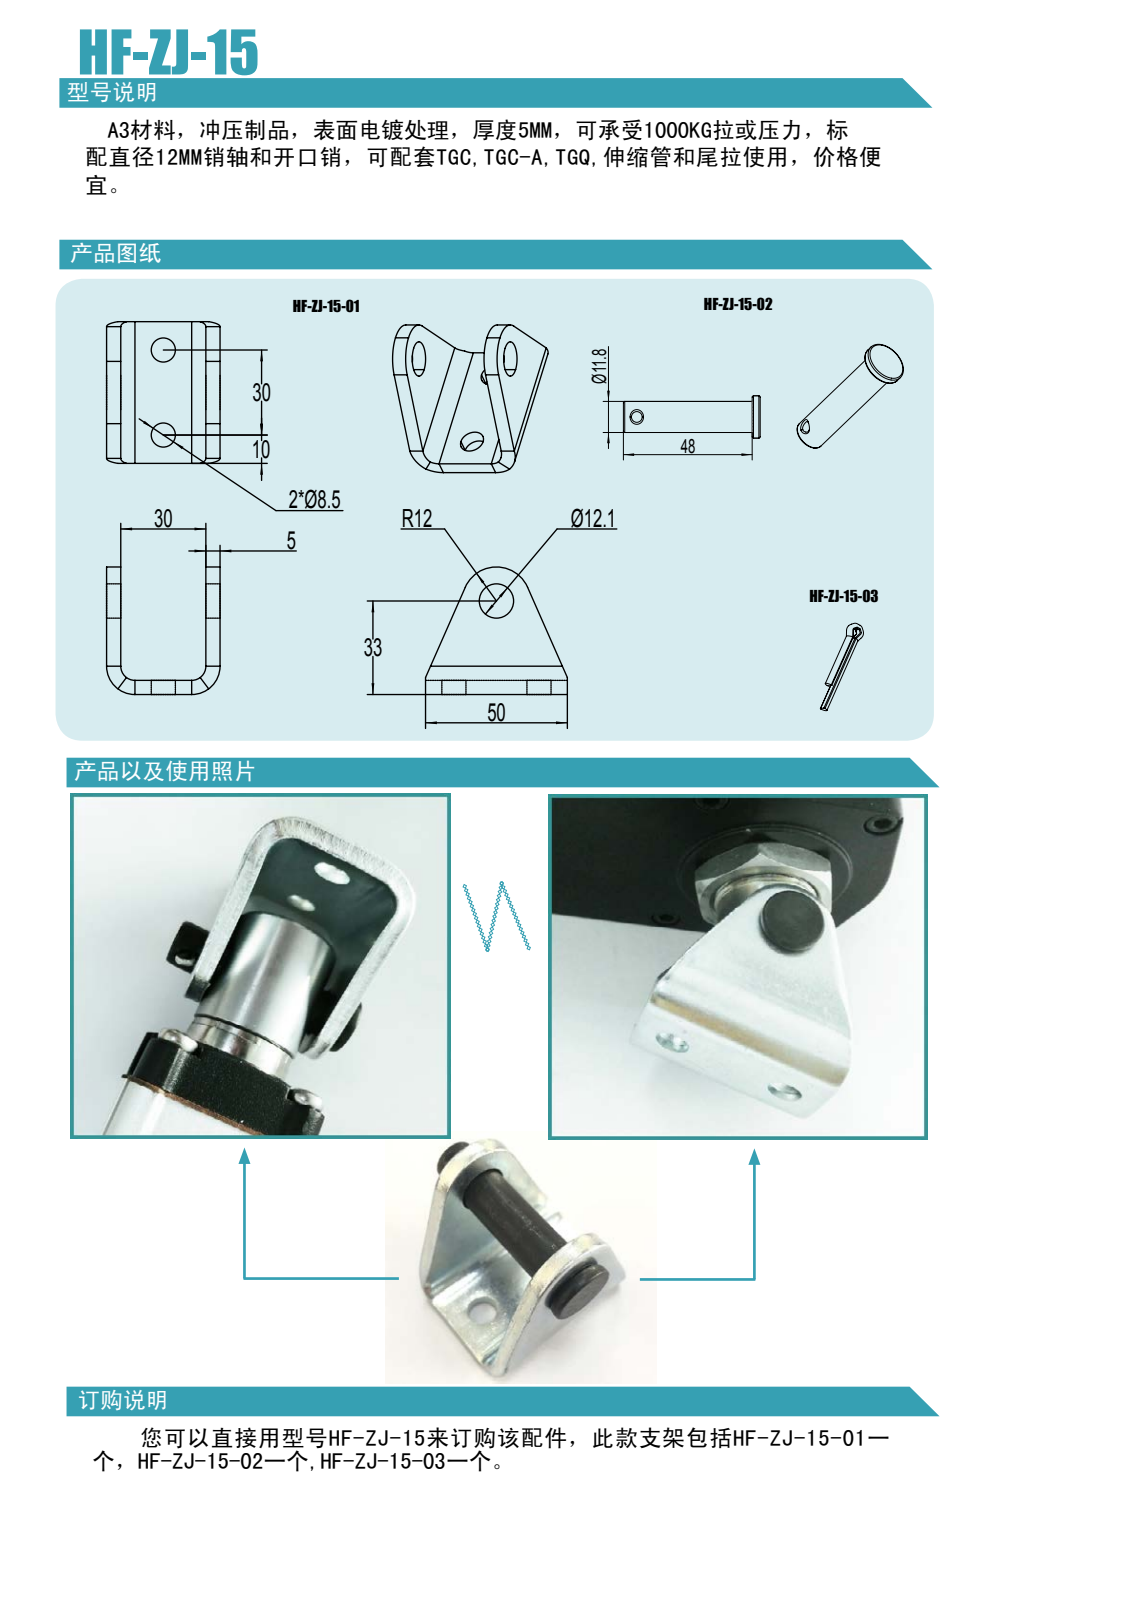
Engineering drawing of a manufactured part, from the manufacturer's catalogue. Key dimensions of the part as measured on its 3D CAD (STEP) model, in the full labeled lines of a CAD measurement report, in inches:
Part name (STEP PRODUCT): ZJ-15
STEP written by: PRO/ENGINEER BY PARAMETRIC TECHNOLOGY CORPORATION, 2008380 (CONFIG_CONTROL_DESIGN)
Units: inches
Bodies: 1 solid, 36 faces (16 planar, 16 cylindrical, 4 other)
Overall size (bounding box): 1.969 × 1.772 × 1.575
Volume: 1.203 in³ · Surface area: 15.28 in²
Round holes (diameter × count): ⌀0.335 ×2, ⌀0.476 ×1
Partial cylindrical surfaces — rounded edges, fillets, slot ends (radius × count): R0.197 ×2, R0.394 ×2, R0.472 ×1
Main face-to-face distances: 0.197, 1.378, 1.575, 1.181, 1.969
Hole centre spacings: 1.181
